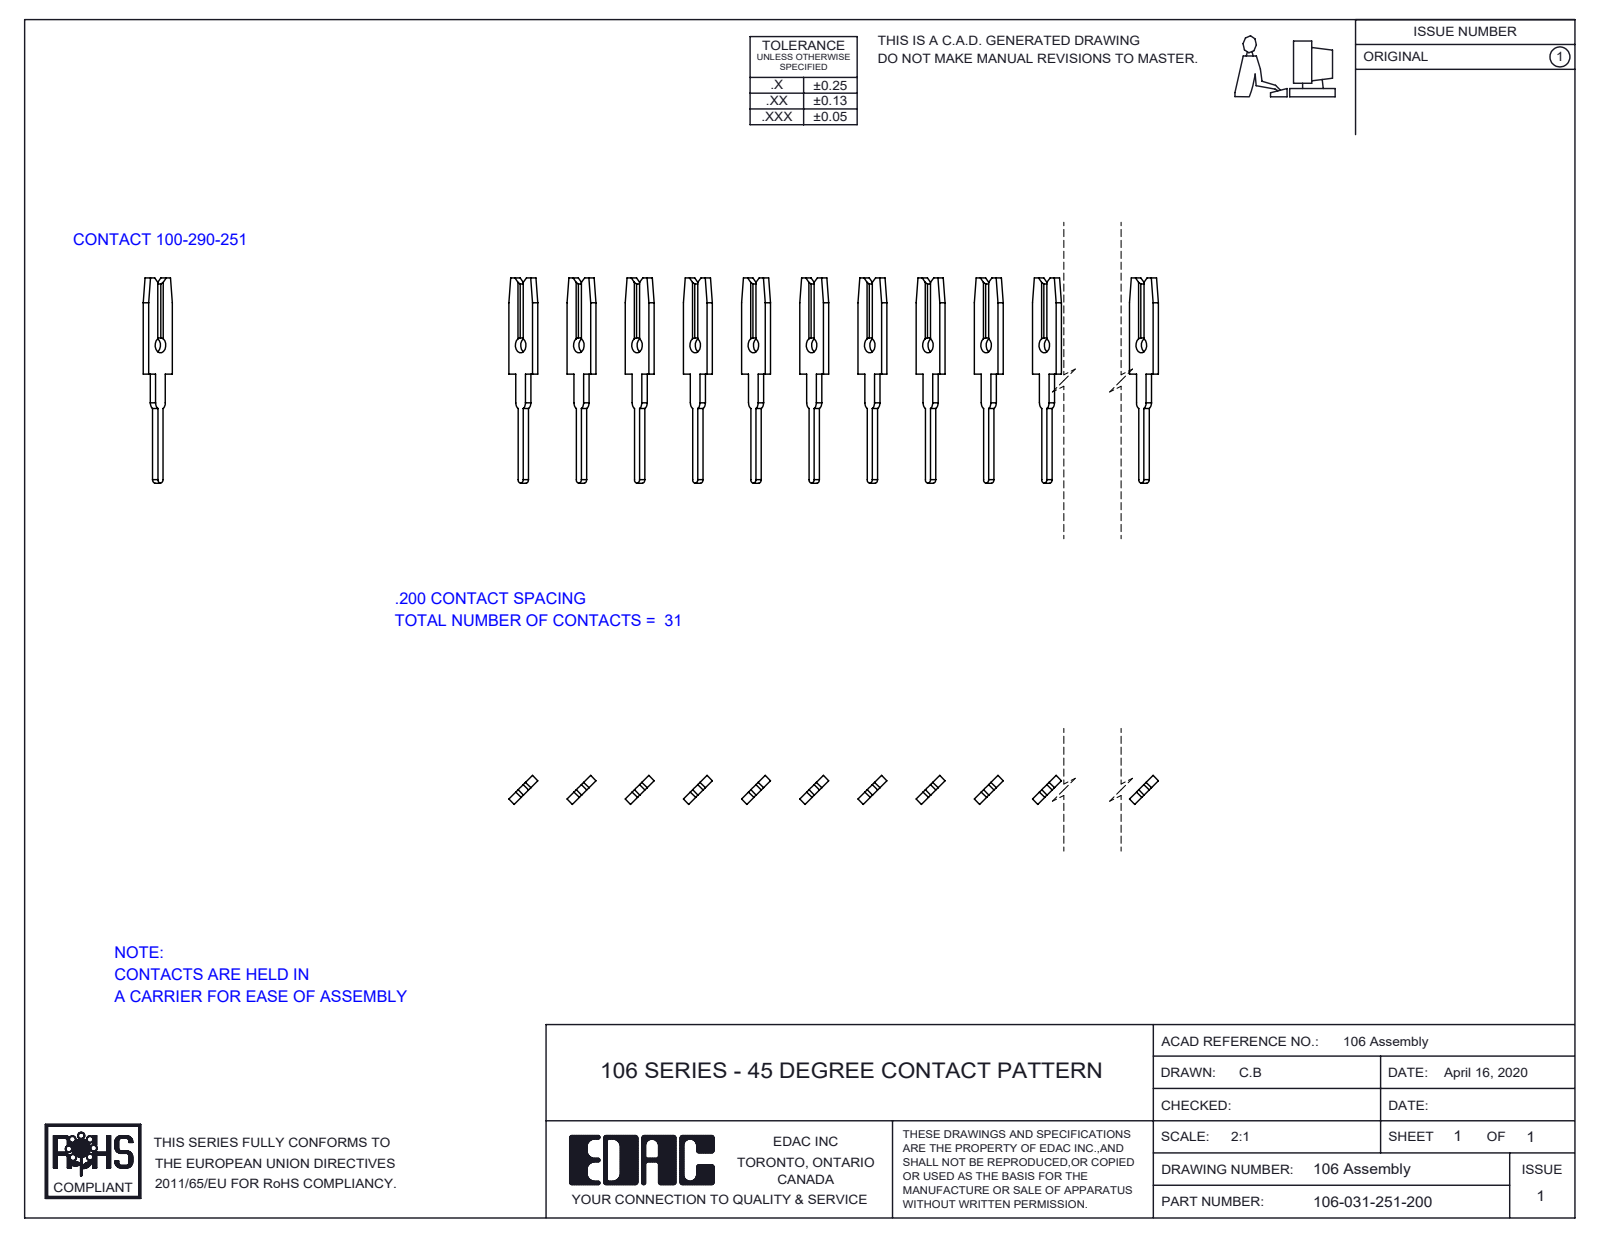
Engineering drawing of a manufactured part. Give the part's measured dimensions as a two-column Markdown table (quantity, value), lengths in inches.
| quantity | value |
| --- | --- |
| part name | 100-290-001_100-290-251; 106-031-251-200 |
| STEP written by | SolidWorks 2016 (CONFIG_CONTROL_DESIGN) |
| units | inches |
| bodies | 31 solids, 868 faces (682 planar, 186 cylindrical, 0 other) |
| overall size | 6.1 × 0.705 × 0.1 |
| volume | 0.035 in³ |
| surface area | 4.318 in² |
| round holes (diameter × count) | 0.052 × 31 |
| partial cylindrical surfaces (radius × count) | 0.012 × 31, 0.024 × 31 |
| main face-to-face distances | 0.141, 0.848, 0.283, 0.707, 0.99, 0.566, 0.424, 1.131, 0.424, 1.556 |
| hole center spacings | 0.141, 0.283, 0.424, 0.848, 1.839, 0.99, 1.556, 1.697 |
